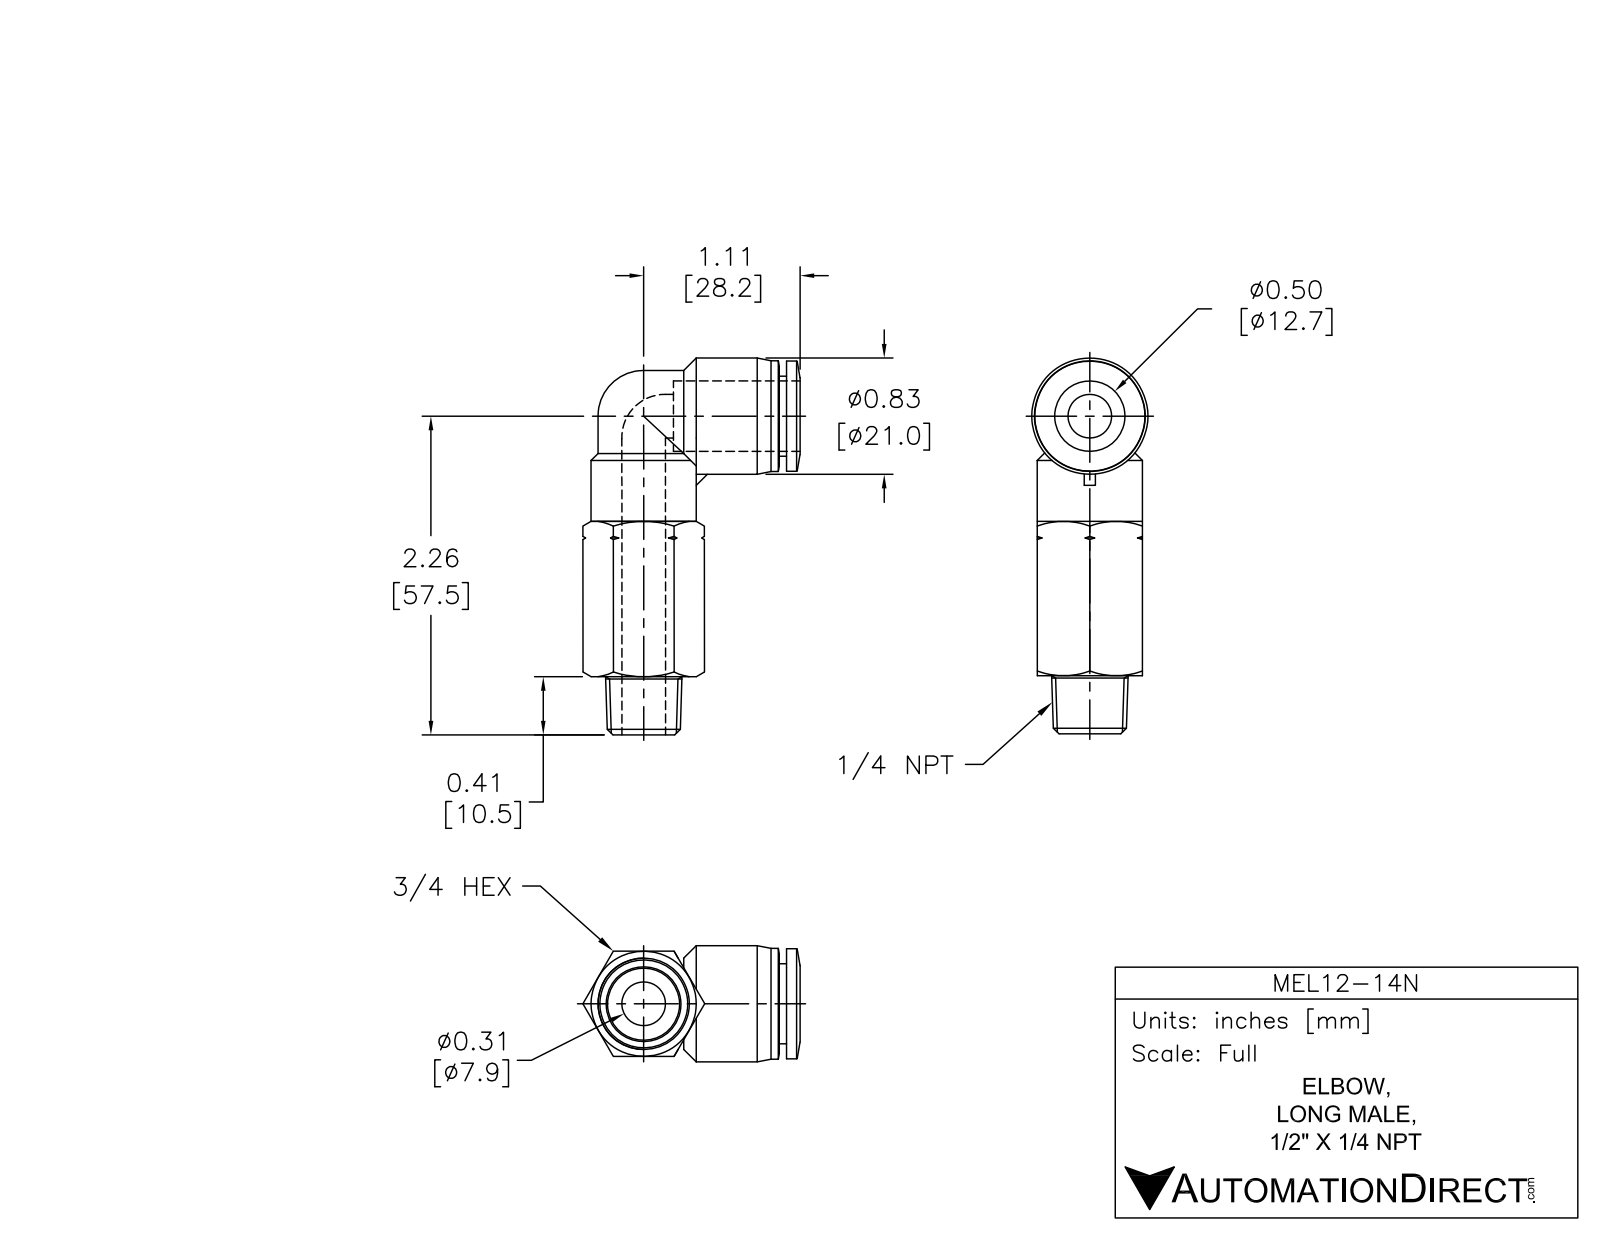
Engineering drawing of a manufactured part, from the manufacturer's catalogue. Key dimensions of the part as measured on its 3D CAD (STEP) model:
Part name (STEP PRODUCT): MEL12-14N
STEP written by: SolidWorks 2015 (AUTOMOTIVE_DESIGN)
Units: inches
Bodies: 1 solid, 85 faces (14 planar, 20 cylindrical, 51 other)
Overall size (bounding box): 2.677 × 1.544 × 0.827
Volume: 1.034 in³ · Surface area: 12.84 in²
Round holes (diameter × count): ⌀0.315 ×2, ⌀0.51 ×1
Round bosses / shafts (diameter × count): ⌀0.65 ×2, ⌀0.827 ×1, ⌀0.787 ×1, ⌀0.783 ×1, ⌀0.748 ×1, ⌀0.569 ×1
Main face-to-face distances: 0.748, 0.051, 0.762, 0.813, 0.413, 0.335, 0.079
